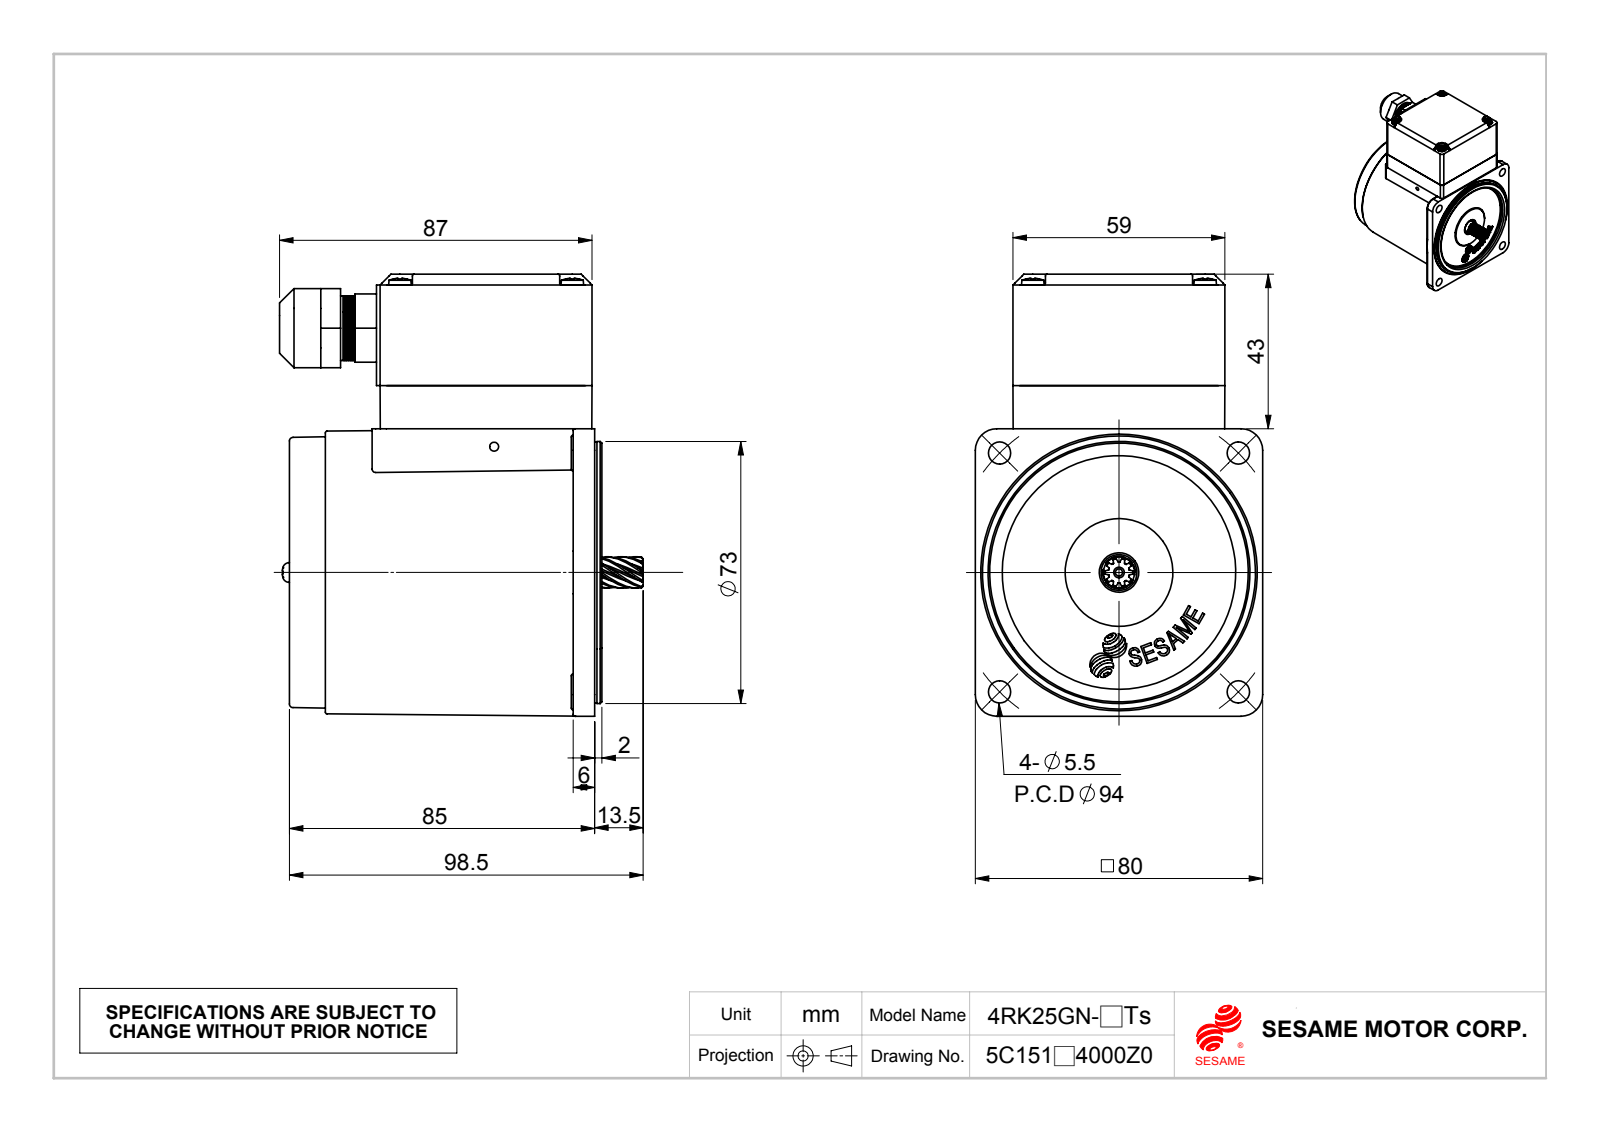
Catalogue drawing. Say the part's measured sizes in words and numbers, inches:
The part is named "成品180度; 25GN_Default; 펥짰웰찿M4즤40x1t_Default; M425TsA-RK_鑽孔攻牙 (+2 more)". Its 3-D file was written by "SolidWorks 2010 (CONFIG_CONTROL_DESIGN)". It is 14 solids with 2772 faces: 314 planar, 977 cylindrical and 1481 other. Overall it measures 4.843 by 3.986 by 3.15 inches. Its volume is 15.35 cubic inches and its surface area 164.2 square inches. Round holes: 4 of diameter 0.13, 4 of diameter 0.138, 4 of diameter 0.154, 4 of diameter 0.165, 4 of diameter 0.169, 4 of diameter 0.244, 3 of diameter 0.098, 2 of diameter 0.157, 2 of diameter 0.433, 1 of diameter 0.079, 1 of diameter 0.472, 1 of diameter 0.571. Round bosses or shafts: 6 of diameter 0.118, 4 of diameter 0.248, 2 of diameter 0.217, 1 of diameter 2.871, 1 of diameter 2.856, 1 of diameter 1.575, 1 of diameter 1.457, 1 of diameter 0.866. Partial cylindrical surfaces (rounded edges, fillets, slot ends): 12 of radius 0.02, 12 of radius 0.079, 8 of radius 0.012, 8 of radius 0.024, 8 of radius 0.046, 8 of radius 0.051, 8 of radius 0.089, 6 of radius 0.157. The main face-to-face distances are 0.472, 0.039, 3.307, 0.059, 3.248, 0.02, 0.118, 0.03, 3.287, 3.15. The hole center spacings are 1.942, 0.591, 0.452, 0.835, 1.091, 1.259, 1.492, 1.85.
